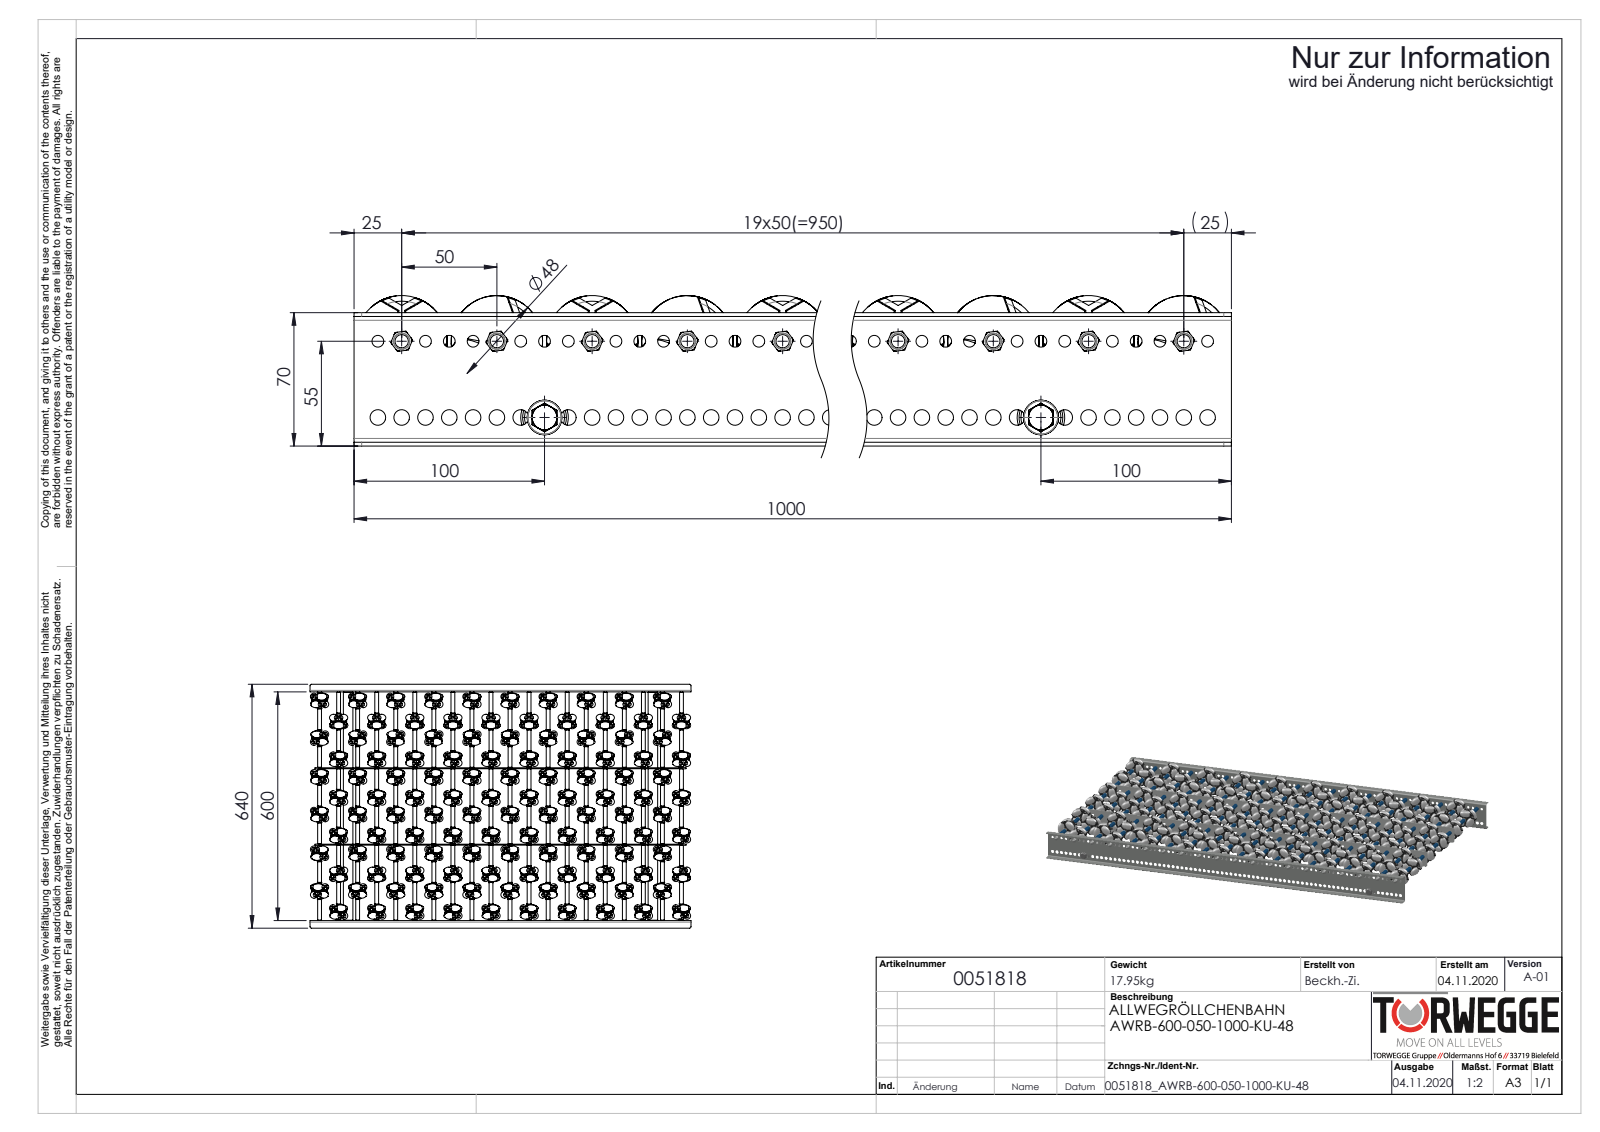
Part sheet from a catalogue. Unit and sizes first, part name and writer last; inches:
Units: inches
Overall size (bounding box): 39.37 × 25.197 × 3.11
Round holes (diameter × count): ⌀0.146 ×720, ⌀0.165 ×720, ⌀0.244 ×79, ⌀0.323 ×79, ⌀0.256 ×39, ⌀0.194 ×20, ⌀0.331 ×20, ⌀0.268 ×2, ⌀0.827 ×2
Round bosses / shafts (diameter × count): ⌀0.157 ×720, ⌀0.146 ×635, ⌀0.315 ×22, ⌀1.854 ×20, ⌀1.654 ×20, ⌀0.433 ×20, ⌀0.394 ×20, ⌀0.276 ×20
Partial cylindrical surfaces — rounded edges, fillets, slot ends (radius × count): R0.157 ×8, R0.079 ×4, R0.197 ×4
Main face-to-face distances: 0.079, 23.701, 7.894, 0.098, 2.677, 23.622, 23.78, 15.811, 15.685, 7.917
Hole centre spacings: 1.42, 1.419, 3.937, 1.42, 1.969, 1.419, 7.874, 1.22
Volume: 399.2 in³ · Surface area: 6 808 in²
Bodies: 1994 solids, 35048 faces (12252 planar, 13532 cylindrical, 9264 other)
Part name (STEP PRODUCT): S108767_Längstraverse-42x2,5-AWR_L1000; 0019730_Tragrollenrohr-Ø10x1,75KU_KFG_0019730_L=54; 0019719_Gewindestange-M6_L=620; 0027528_BUCHSE-HOHLNIETE ZU AWR48 (+8 more)
STEP written by: SolidWorks 2020 (AUTOMOTIVE_DESIGN)
